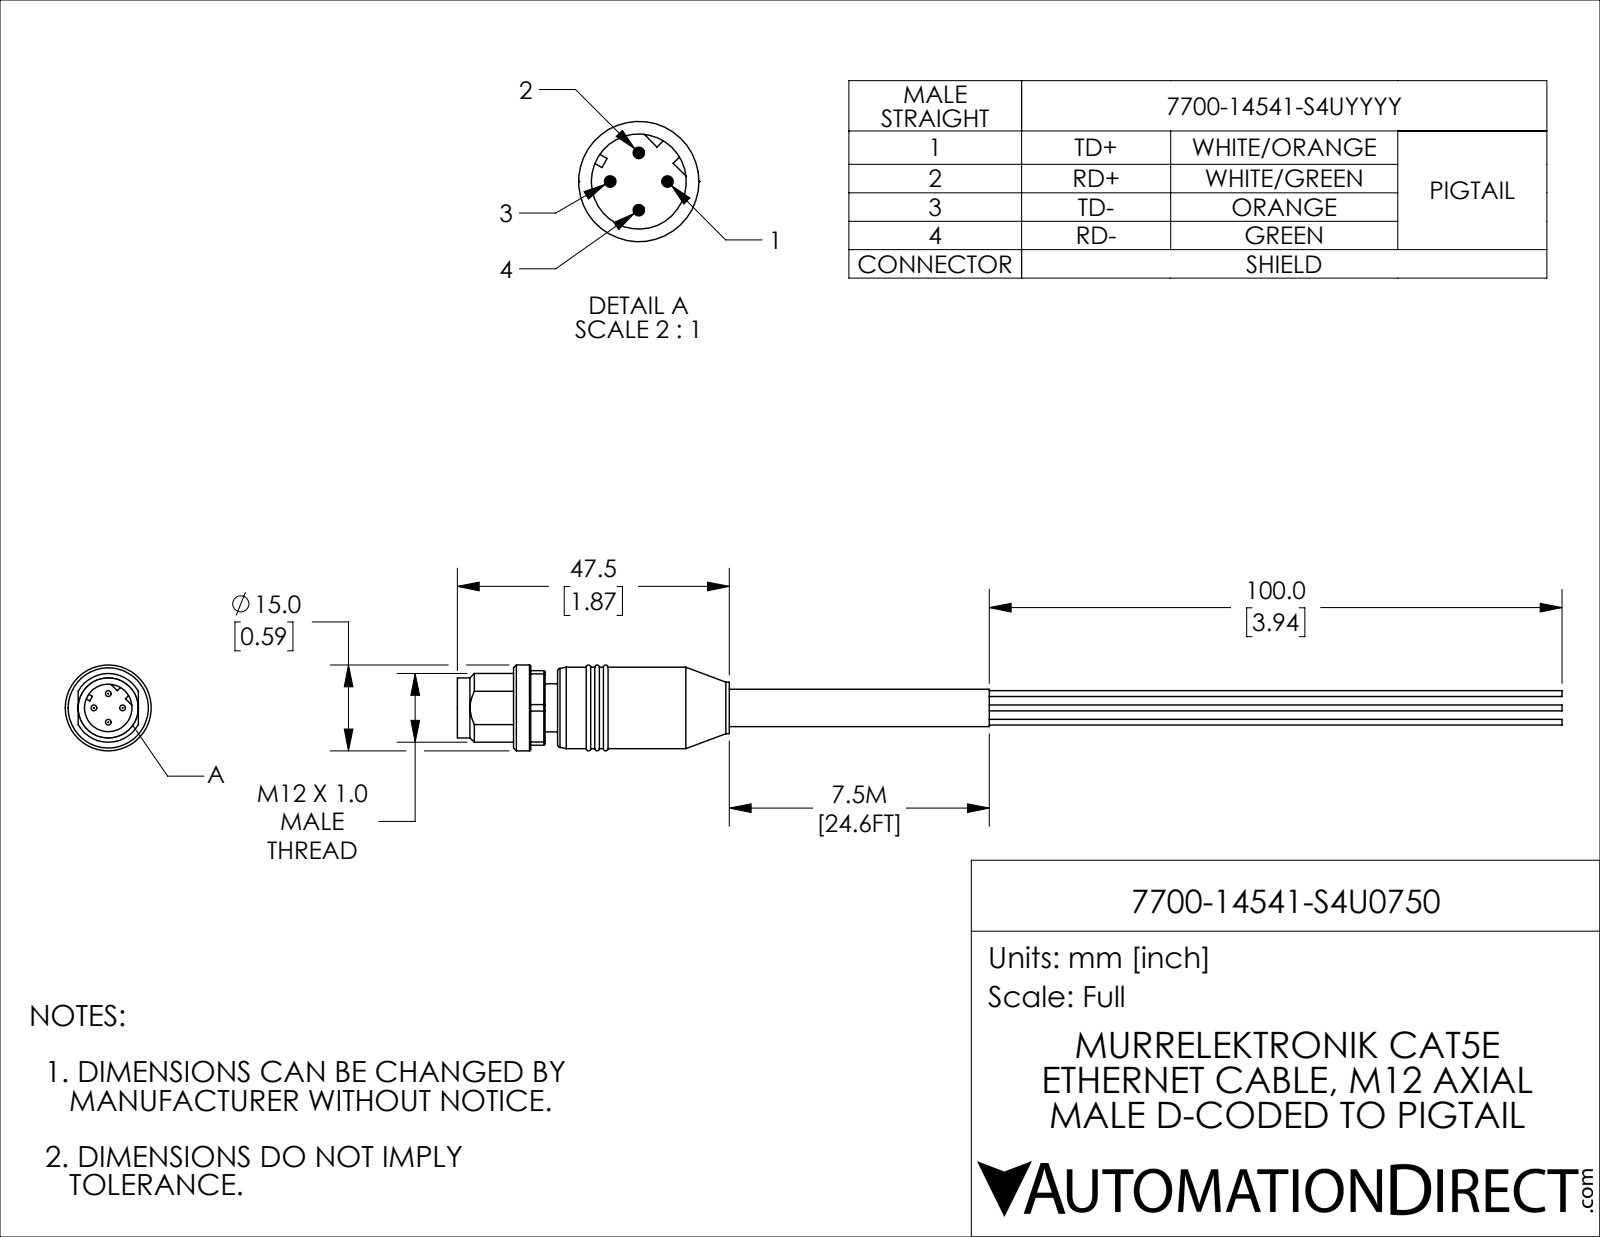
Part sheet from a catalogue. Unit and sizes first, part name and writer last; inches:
Units: inches
Overall size (bounding box): 7.594 × 0.591 × 0.591
Round holes (diameter × count): ⌀0.327 ×1
Round bosses / shafts (diameter × count): ⌀0.039 ×4, ⌀0.591 ×1, ⌀0.559 ×1, ⌀0.413 ×1, ⌀0.354 ×1, ⌀0.331 ×1, ⌀0.256 ×1
Partial cylindrical surfaces — rounded edges, fillets, slot ends (radius × count): R0.236 ×1, R0.283 ×1
Main face-to-face distances: 0.087, 0.035, 0.252, 0.339, 0.217, 0.303, 0.512, 0.413, 0.35, 0.386
Volume: 0.473 in³ · Surface area: 7.675 in²
Bodies: 1 solid, 125 faces (40 planar, 45 cylindrical, 40 other)
Part name (STEP PRODUCT): 7700-14541-S4U0750
STEP written by: SolidWorks 2021 (CONFIG_CONTROL_DESIGN)
